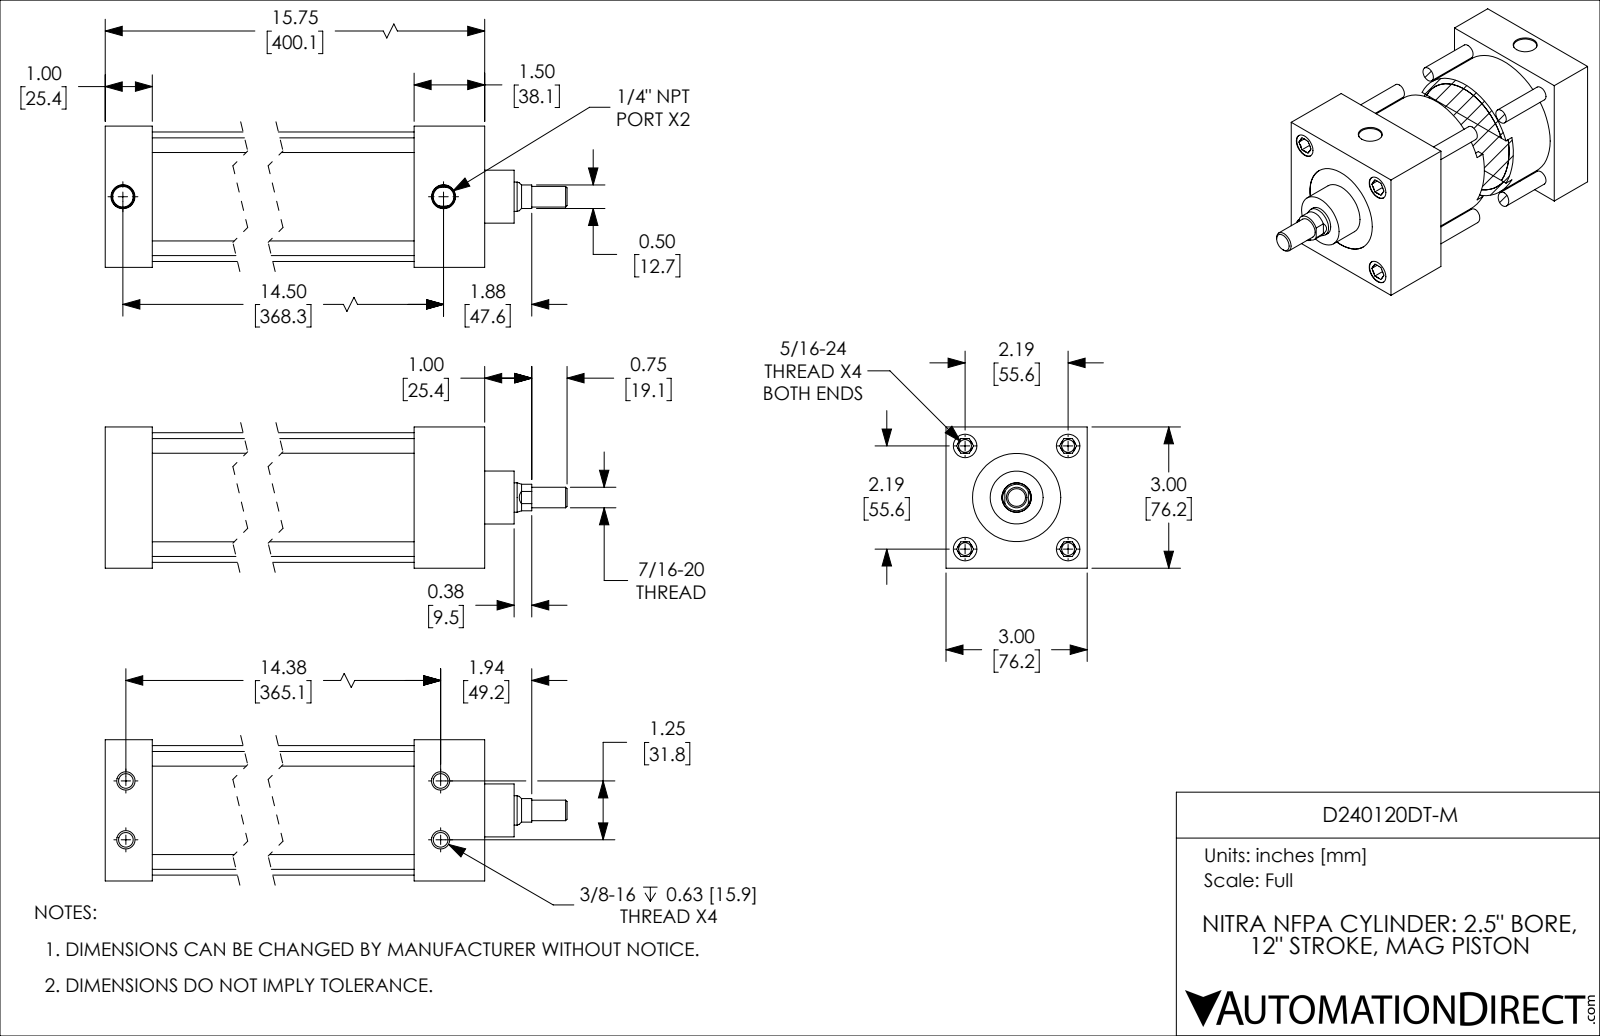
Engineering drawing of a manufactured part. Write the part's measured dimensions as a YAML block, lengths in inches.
part_name: "D240120DT-M_BODY; D240120DT-M; D240120DT-M_PISTON_KK1"
step_written_by: "SolidWorks 2019 (CONFIG_CONTROL_DESIGN)"
units: inches
bodies: {solids: 2, faces: 200, planar: 58, cylindrical: 62, other: 80}
overall_size: [17.5, 3, 3]
volume: 49.75
surface_area: 400.7
round_holes:
  - {diameter: 0.272, count: 4}
  - {diameter: 0.313, count: 4}
  - {diameter: 0.5, count: 4}
  - {diameter: 0.438, count: 2}
  - {diameter: 0.626, count: 1}
  - {diameter: 1.875, count: 1}
  - {diameter: 2.501, count: 1}
round_bosses_or_shafts:
  - {diameter: 0.312, count: 4}
  - {diameter: 2.751, count: 1}
  - {diameter: 2.499, count: 1}
  - {diameter: 1.125, count: 1}
  - {diameter: 0.624, count: 1}
  - {diameter: 0.437, count: 1}
partial_cylinders:
  - {radius: 0.281, count: 1}
face_to_face_distances: [3, 1, 14.25, 13.25, 15.75, 14.75, 1.5, 1.25, 2.25, 12]
hole_center_spacings: [1.548, 2.19, 14.451, 0.628, 0.628, 1.25, 3.097, 14.375]
